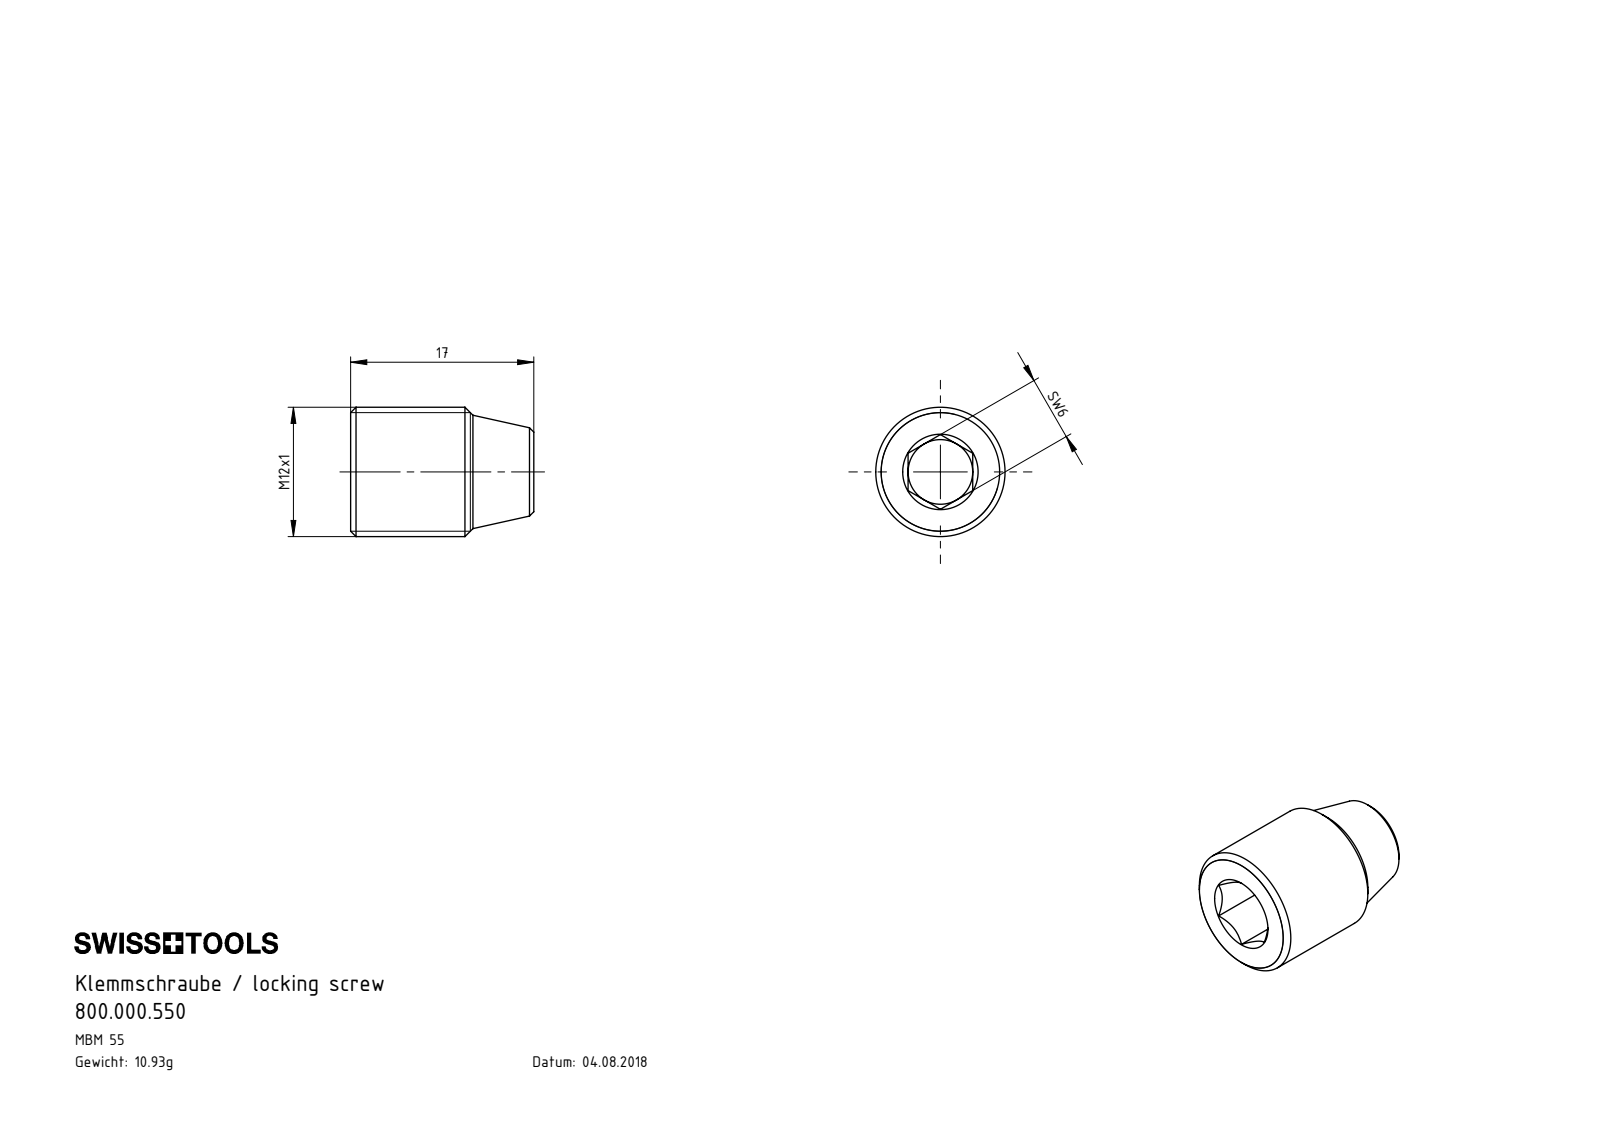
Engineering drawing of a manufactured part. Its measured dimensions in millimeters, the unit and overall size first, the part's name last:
Units: millimetres
Overall size (bounding box): 17 × 12 × 12
Round holes (diameter × count): ⌀6 ×1
Round bosses / shafts (diameter × count): ⌀12 ×1
Main face-to-face distances: 6, 17, 10, 7
Volume: 1 393 mm³ · Surface area: 916 mm²
Bodies: 1 solid, 22 faces (14 planar, 2 cylindrical, 6 other)
Part name (STEP PRODUCT): 800.000.550
STEP written by: SolidWorks 2017 (AUTOMOTIVE_DESIGN)
